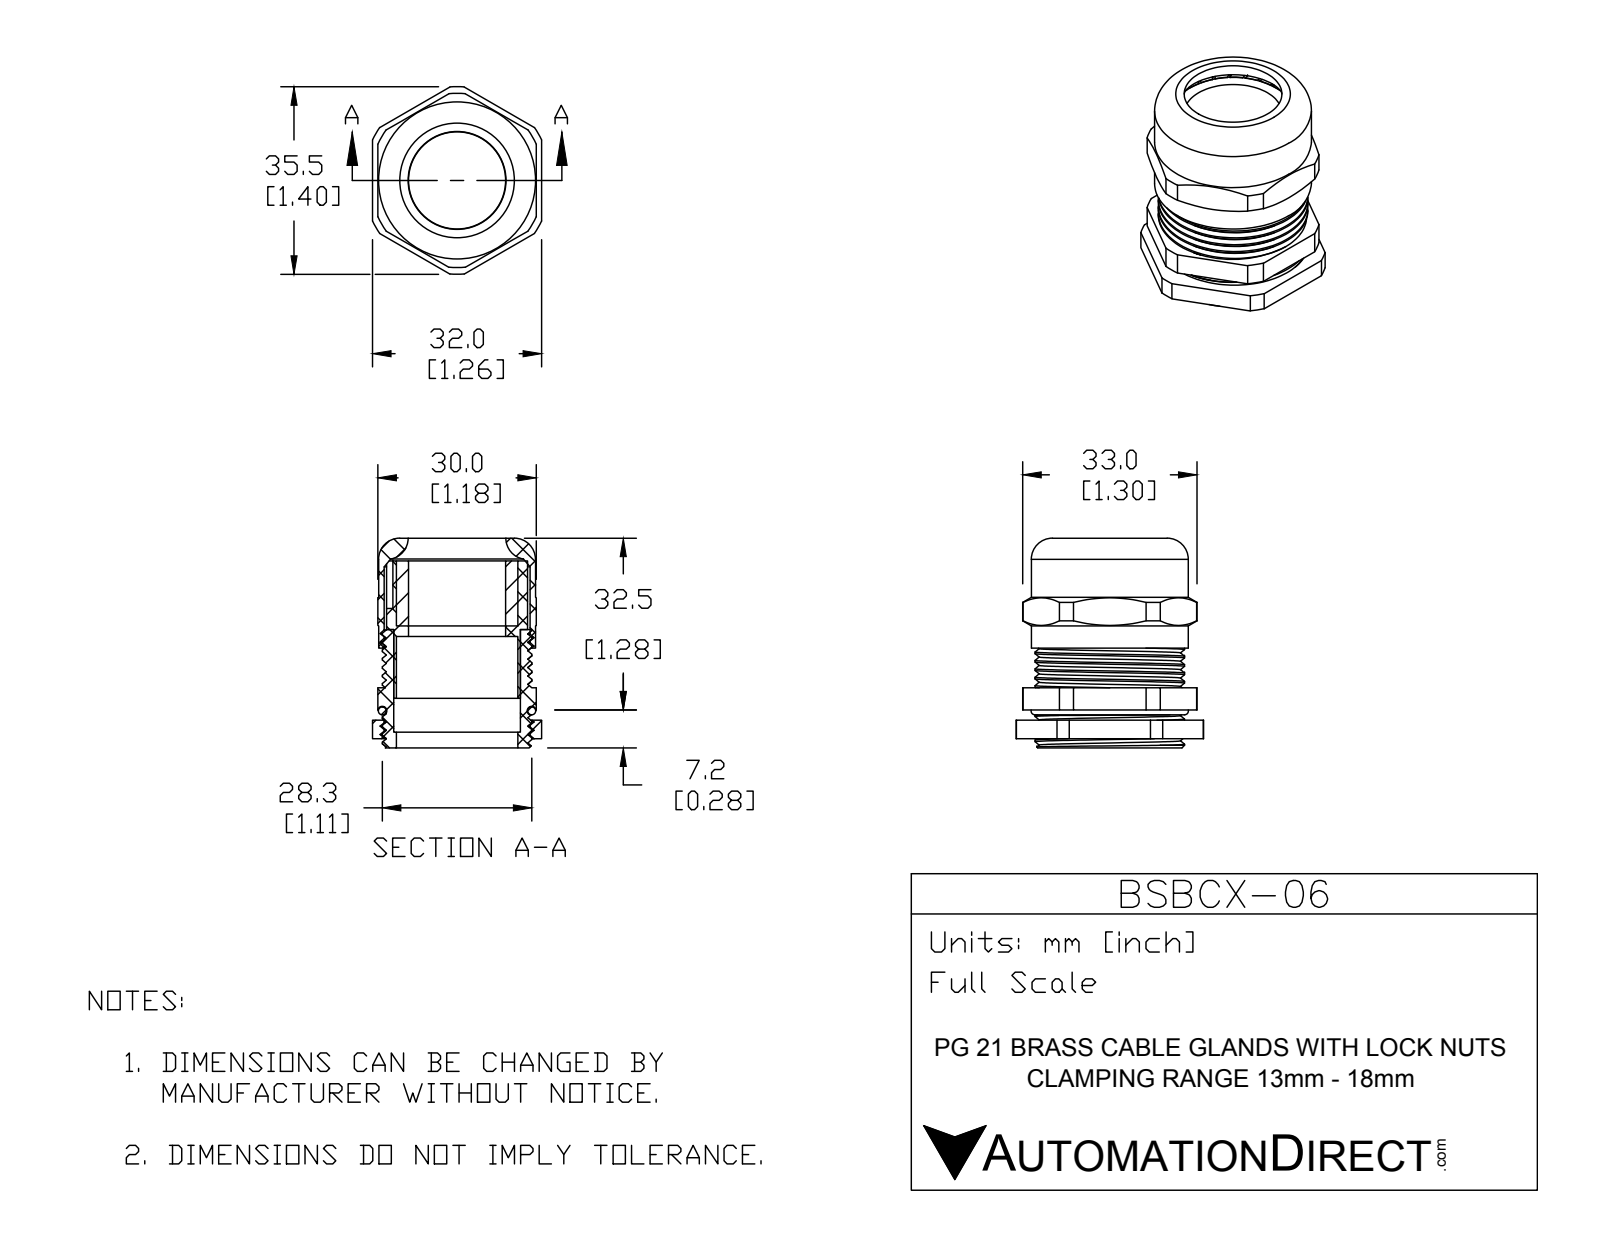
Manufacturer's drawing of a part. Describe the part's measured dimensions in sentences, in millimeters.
The part is named "BSBCX-06". Its 3-D file was written by "SolidWorks 2015 (CONFIG_CONTROL_DESIGN)". It is 6 solids with 241 faces: 134 planar, 77 cylindrical and 30 other. Overall it measures 39.7 by 35.5 by 32 millimeters. Its volume is 12 487 cubic millimeters and its surface area 18 373 square millimeters. Round holes: 1 of diameter 18.4, 1 of diameter 23, 1 of diameter 24, 1 of diameter 27.63. Round bosses or shafts: 1 of diameter 29.7, 1 of diameter 28.3, 1 of diameter 26.7. Partial cylindrical surfaces (rounded edges, fillets, slot ends): 1 of radius 16.5, 1 of radius 17.75. The main face-to-face distances are 0.5, 30, 1, 31, 3.5, 17.15, 13, 11.7, 12.3, 0.7.
